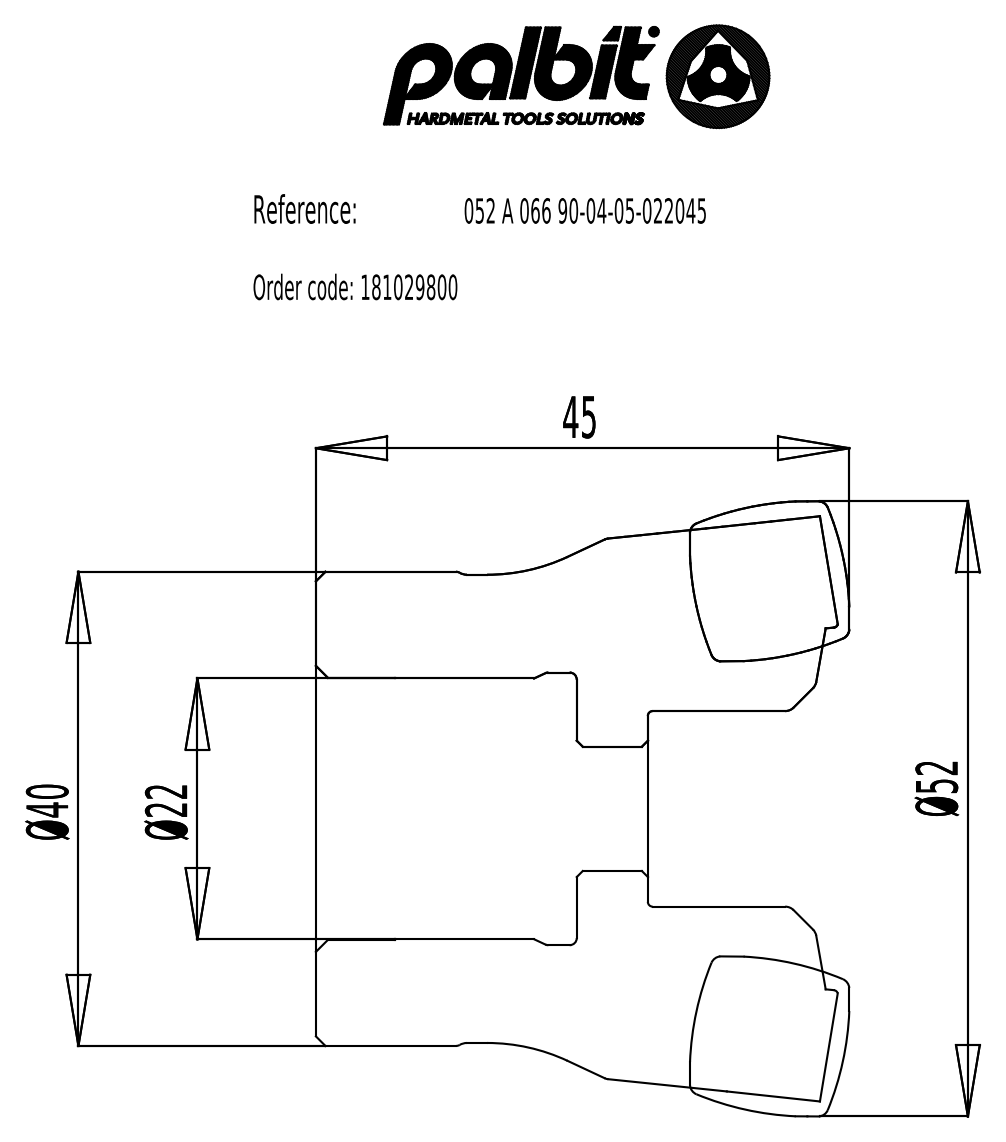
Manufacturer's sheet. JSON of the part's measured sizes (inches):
{"part_name": "CUT PROFILE - 181029800; CUT^CUT PROFILE - 181029800; NOCUT^CUT PROFILE - 181029800", "step_written_by": "SolidWorks 2015 (CONFIG_CONTROL_DESIGN)", "units": "inches", "bodies": {"solids": 2, "faces": 54, "planar": 6, "cylindrical": 7, "other": 41}, "overall_size": [2.043, 2.043, 1.771], "volume_in3": 4.32, "surface_area_in2": 26.15, "round_holes": [[0.413, 1], [0.65, 1], [0.866, 1], [0.871, 1], [0.906, 1]], "round_bosses_or_shafts": [[1.575, 1], [1.555, 1]], "face_to_face_distances": [1.242, 0.376, 0.866, 0.529, 0.905, 1.771, 0.669, 0.14, 0.236, 1.102]}
